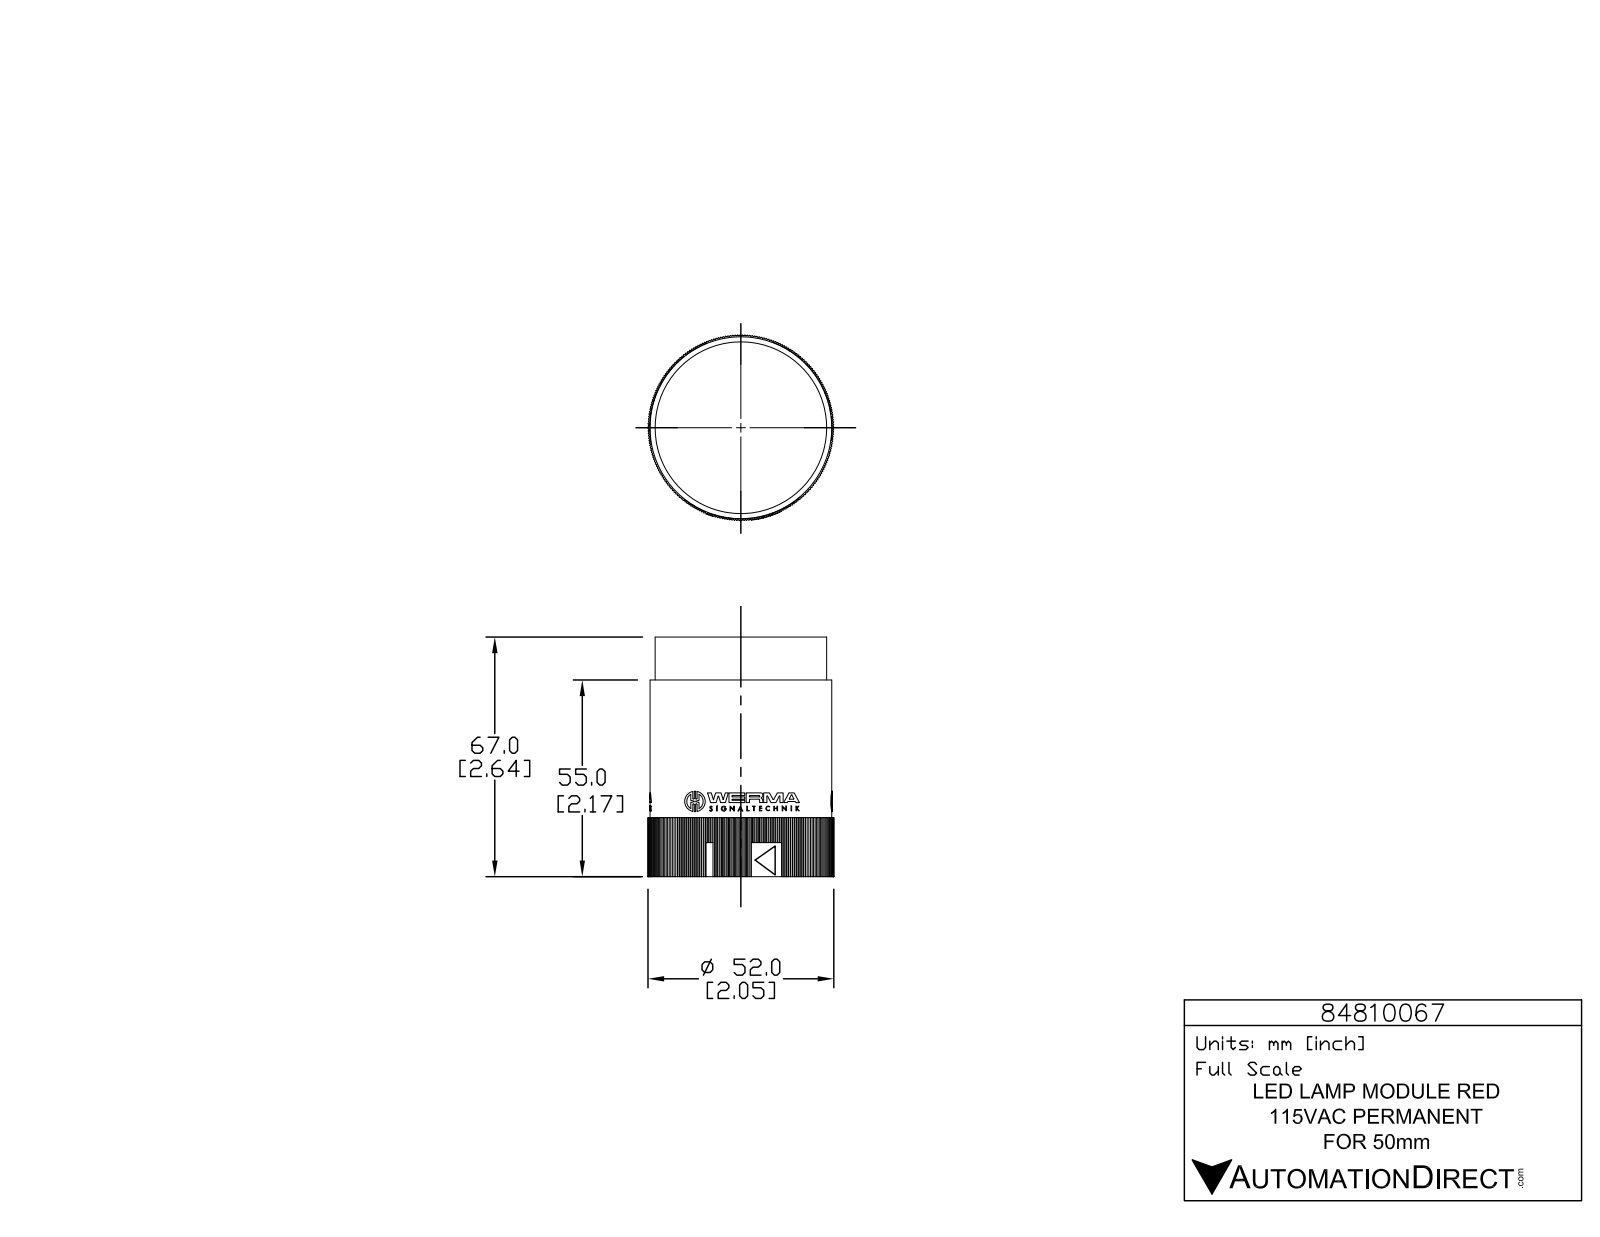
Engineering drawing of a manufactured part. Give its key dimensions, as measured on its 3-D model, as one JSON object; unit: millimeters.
{"part_name": "84810067", "step_written_by": "SolidWorks 2015 (AUTOMOTIVE_DESIGN)", "units": "millimeters", "bodies": {"solids": 1, "faces": 1265, "planar": 1020, "cylindrical": 245, "other": 0}, "overall_size": [67, 52, 52], "volume_mm3": 112600, "surface_area_mm2": 17820, "round_holes": [[1, 3], [48.2, 1]], "round_bosses_or_shafts": [[5.7, 3], [1.4, 3], [50.9, 1], [48, 1]], "partial_cylinders_radius": [[0.2, 6], [0.2, 6], [0.2, 6], [3.3, 6], [0.1, 3], [0.1, 3], [0.2, 3], [0.2, 3]], "face_to_face_distances": [55, 36.3, 36.3, 36.3, 12, 67, 36.3, 36.3, 43, 50.5]}
